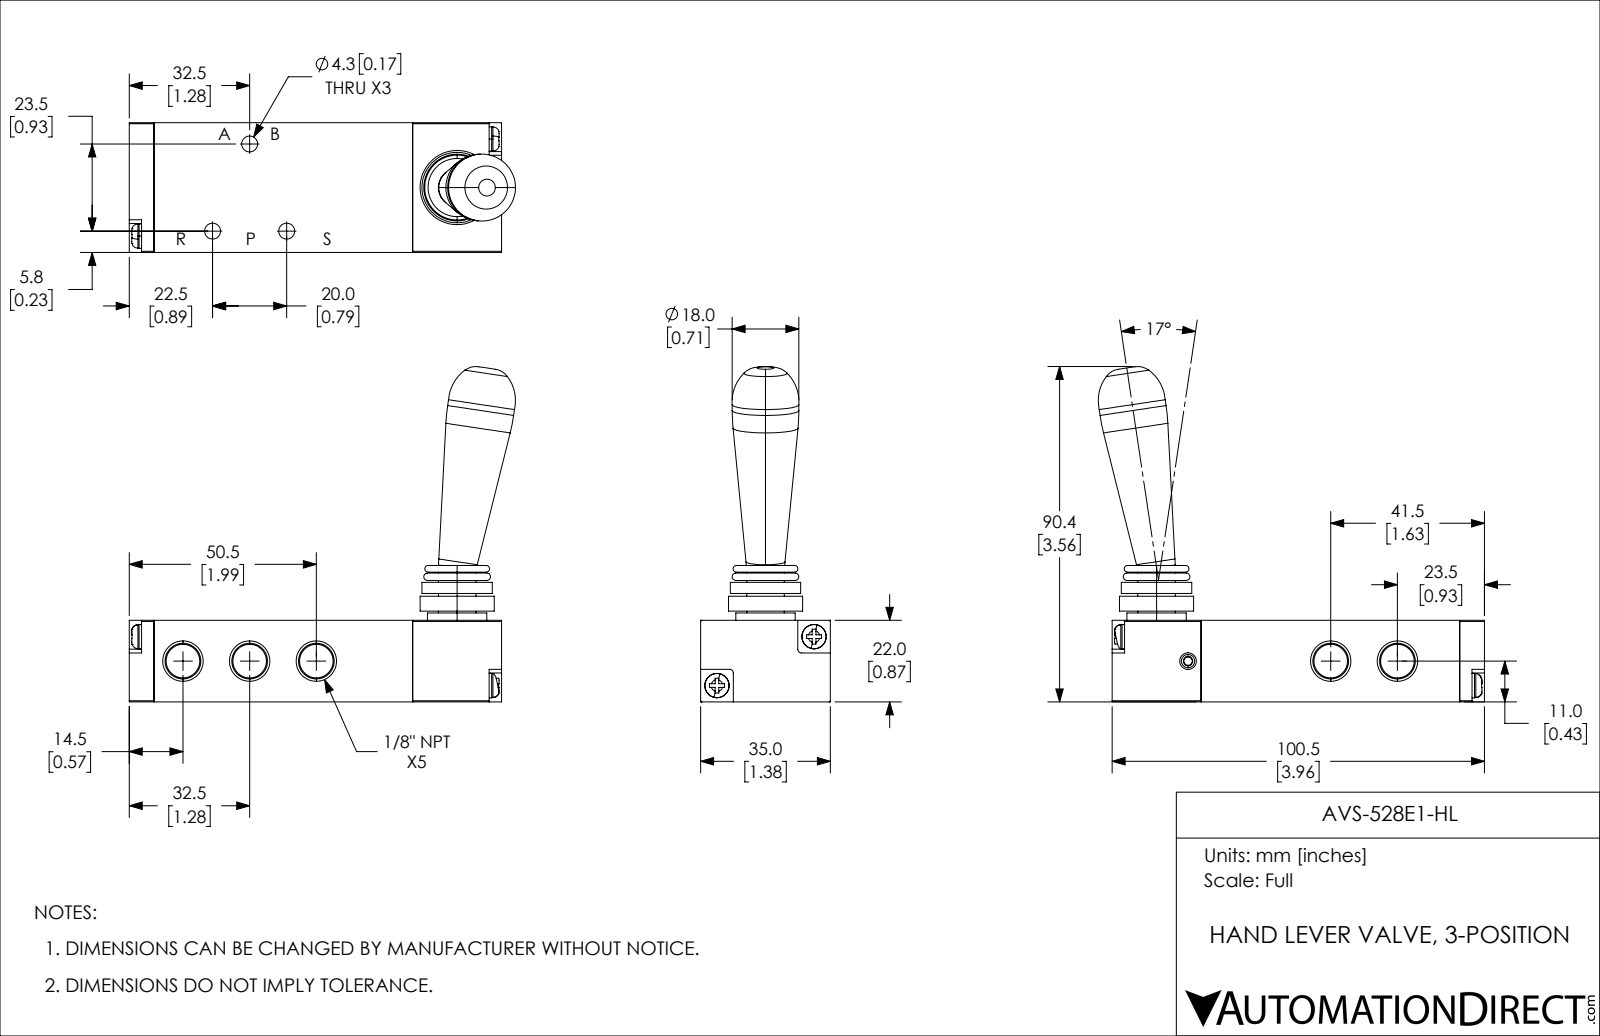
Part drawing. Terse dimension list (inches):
name: AVS-528E1-HL
written by: SolidWorks 2018 (AUTOMOTIVE_DESIGN)
unit: in
bodies: 4 solids, 231 faces (130 planar, 57 cylindrical, 44 other)
size: 4.104 × 3.561 × 1.378
volume: 5.17 in³; area: 37.18 in²
holes: 3× ⌀0.169, 1× ⌀0.177, 1× ⌀0.63
bosses: 4× ⌀0.26, 4× ⌀0.256, 1× ⌀0.787, 1× ⌀0.748, 1× ⌀0.709, 1× ⌀0.399, 1× ⌀0.142
rounds: 4× R0.012, 4× R0.039
face distances: 0.866, 1.378, 2.748, 0.945, 3.693, 0.079, 0.264, 3.957, 3.012, 0.157
hole spacings: 1.006, 0.787, 1.869, 2.253, 2.639
